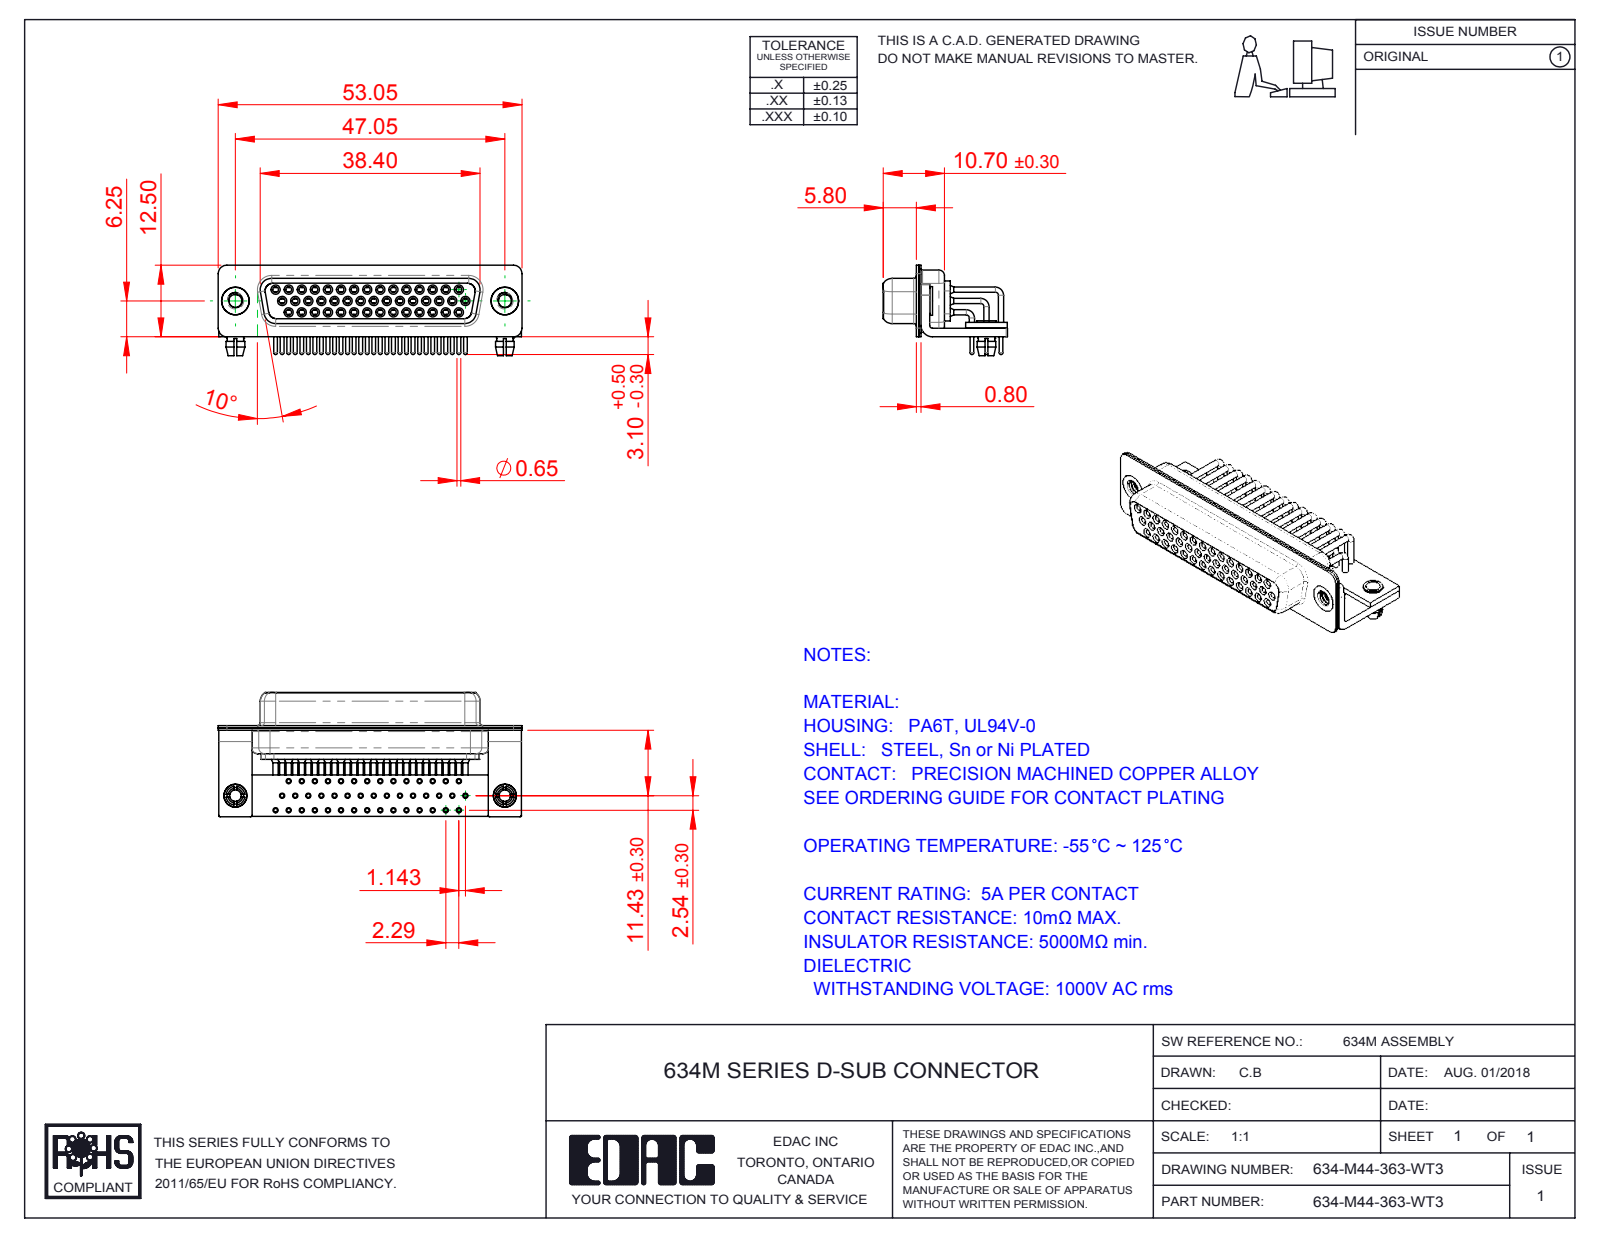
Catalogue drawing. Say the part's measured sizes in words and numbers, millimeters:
The part is named "634M Contact Row 1; 634M Shell Front_44 Contacts; 634M Stabilizer Bracket; 634M Housing_44 Contacts (+7 more)". Its 3-D file was written by "SolidWorks 2016 (CONFIG_CONTROL_DESIGN)". It is 54 solids with 2841 faces: 801 planar, 1291 cylindrical and 749 other. Overall it measures 53.05 by 21.7 by 15.8 millimeters. Its volume is 4 503 cubic millimeters and its surface area 14 836 square millimeters. Round holes: 46 of diameter 2, 44 of diameter 0.9, 44 of diameter 1, 44 of diameter 1.1, 44 of diameter 1.7, 44 of diameter 1.8, 2 of diameter 2.26, 2 of diameter 2.5, 2 of diameter 3.2, 2 of diameter 4, 2 of diameter 4.8. Round bosses or shafts: 44 of diameter 1.6, 44 of diameter 1.5, 44 of diameter 0.9, 44 of diameter 0.65, 2 of diameter 5, 2 of diameter 4.9, 2 of diameter 4, 2 of diameter 3.4. Partial cylindrical surfaces (rounded edges, fillets, slot ends): 16 of radius 0.25, 16 of radius 1.5, 13 of radius 2, 8 of radius 1.35, 8 of radius 1.6, 5 of radius 0.5, 4 of radius 0.6, 4 of radius 0.65. The main face-to-face distances are 0.4, 2.3, 1, 1.9, 0.8, 9.35, 1.45, 8.95, 1.5, 0.85. The hole center spacings are 2.28, 2.29, 4.57, 6.86, 11.43, 3.96, 8.24, 9.14.
